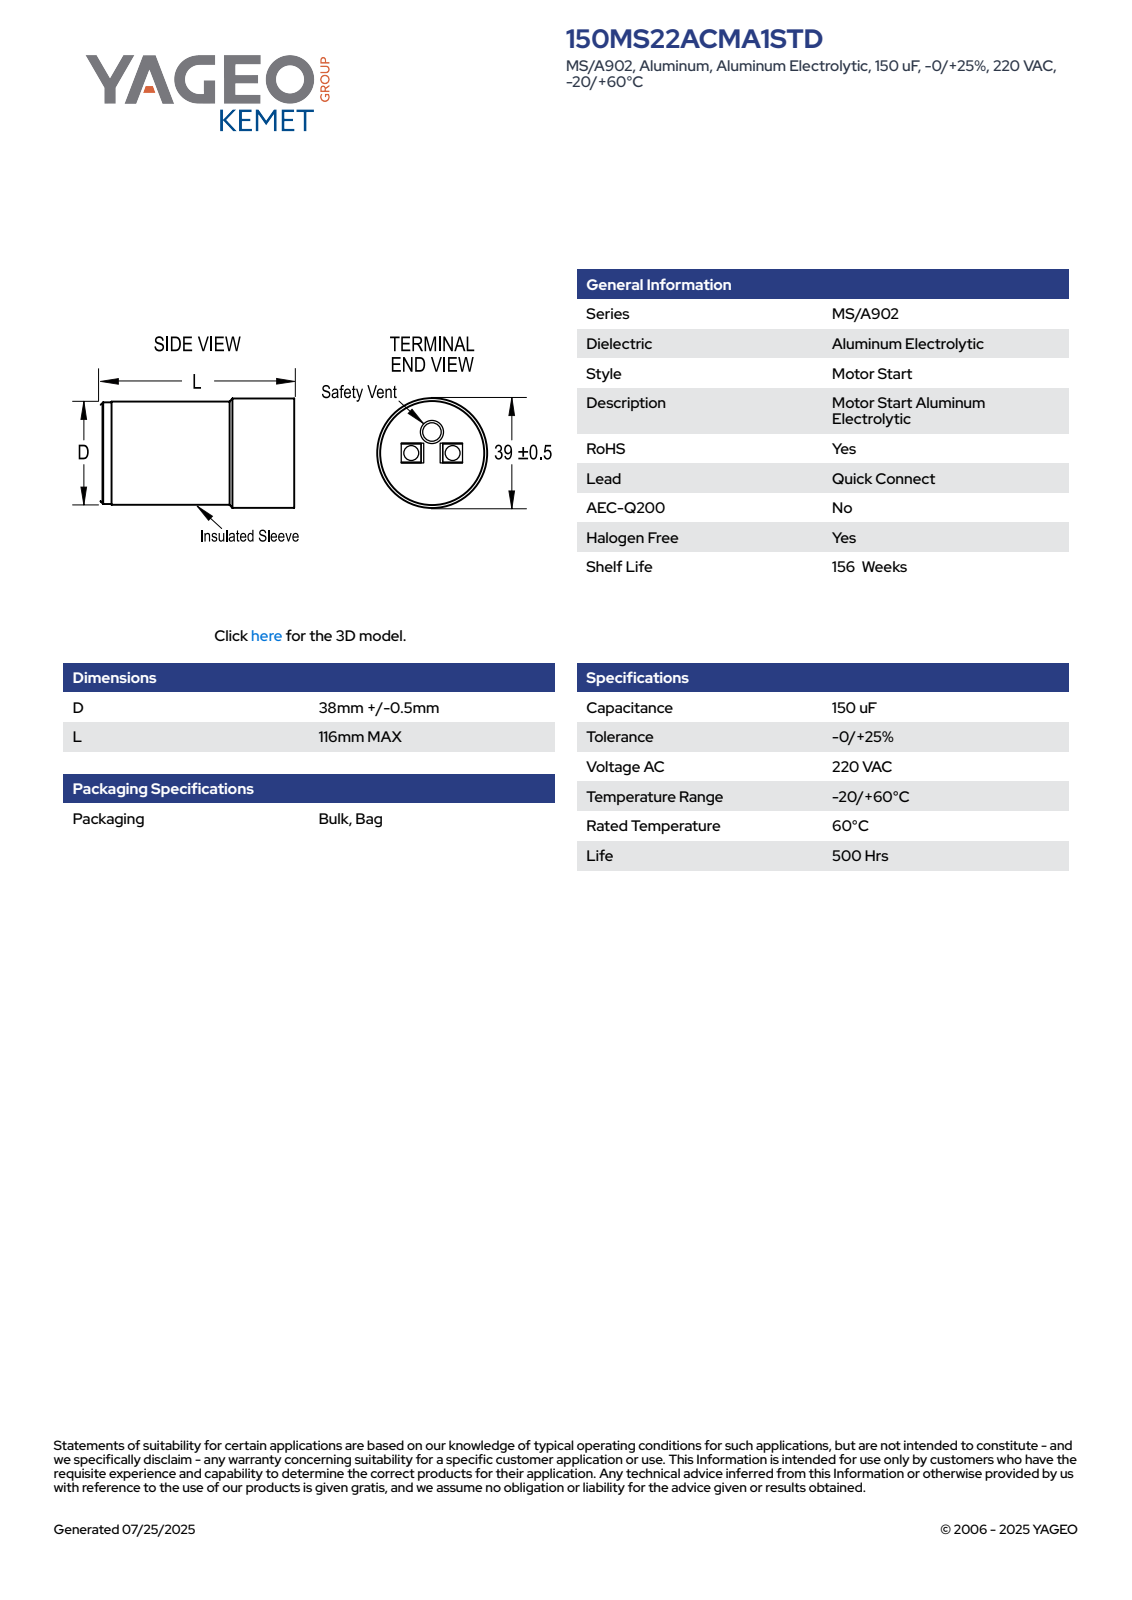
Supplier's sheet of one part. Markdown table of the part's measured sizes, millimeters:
| quantity | value |
| --- | --- |
| part name | CAR_MSMD_38X116_D38.5L116 |
| STEP written by | SolidWorks 2014 (AUTOMOTIVE_DESIGN) |
| units | millimeters |
| bodies | 1 solid, 113 faces (49 planar, 31 cylindrical, 33 other) |
| overall size | 116 × 39.5 × 39.5 |
| volume | 101 590 mm³ |
| surface area | 20 714 mm² |
| round holes (diameter × count) | 1 × 2, 37.4 × 1 |
| round bosses / shafts (diameter × count) | 39.5 × 1, 38.5 × 1, 6.24 × 1, 5.49 × 1 |
| partial cylindrical surfaces (radius × count) | 0.4 × 4, 19.26 × 1 |
| main face-to-face distances | 83.57, 4.7, 116, 32.43, 5, 4.4, 84.02, 0.45, 31.98, 83.87 |
| hole center spacings | 14 |
